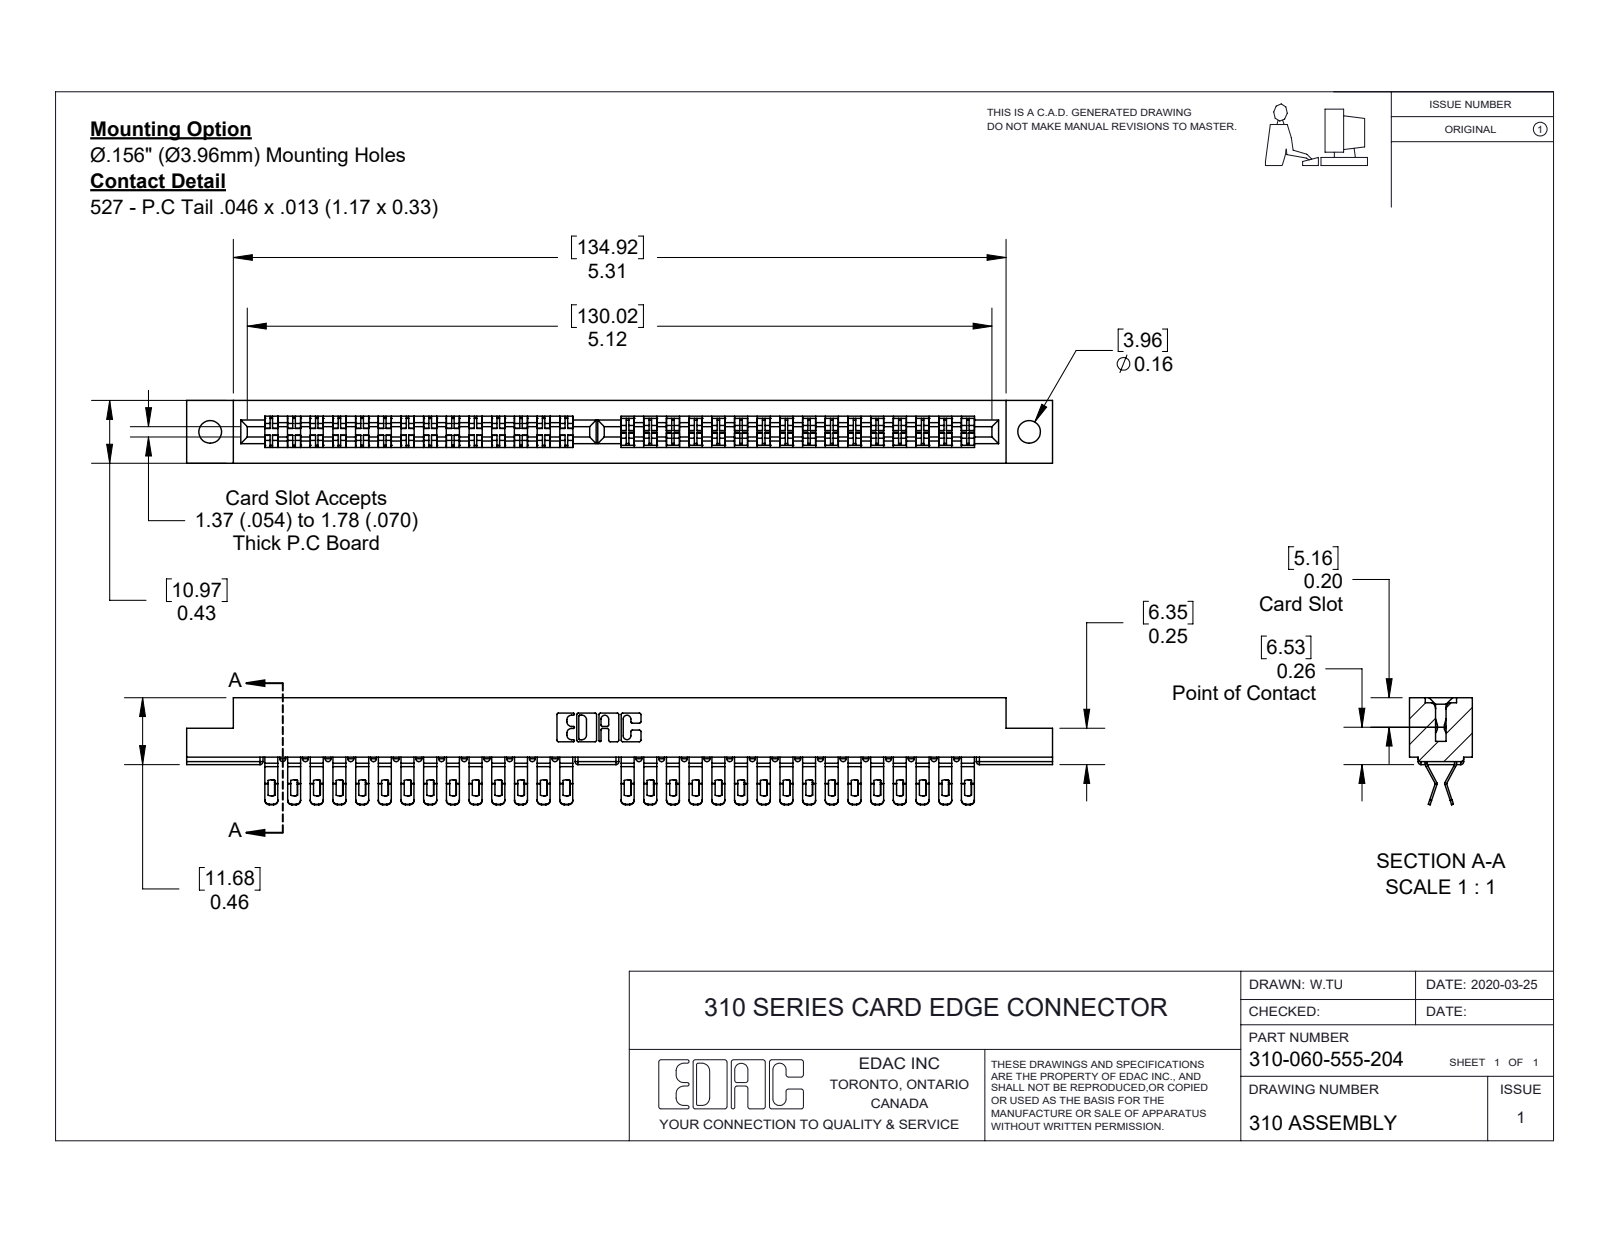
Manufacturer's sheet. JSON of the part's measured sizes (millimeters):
{"part_name": "310-060-555-204; 310 Part_.156 Dia. Hole; 307-290-001_555", "step_written_by": "SolidWorks 2016 (CONFIG_CONTROL_DESIGN)", "units": "millimeters", "bodies": {"solids": 61, "faces": 3826, "planar": 2124, "cylindrical": 1638, "other": 64}, "overall_size": [151.21, 18.69, 10.97], "volume_mm3": 13101, "surface_area_mm2": 18684, "round_holes": [[3.96, 2]], "partial_cylinders_radius": [[0.76, 120], [1.57, 120], [0.51, 98], [0.25, 22], [0.17, 6], [0.8, 6], [0.3, 4], [0.38, 4]], "face_to_face_distances": [0.33, 2.76, 8.22, 0.38, 10.98, 4.75, 5.46, 1.82, 3.14, 7.84], "hole_center_spacings": [143]}
